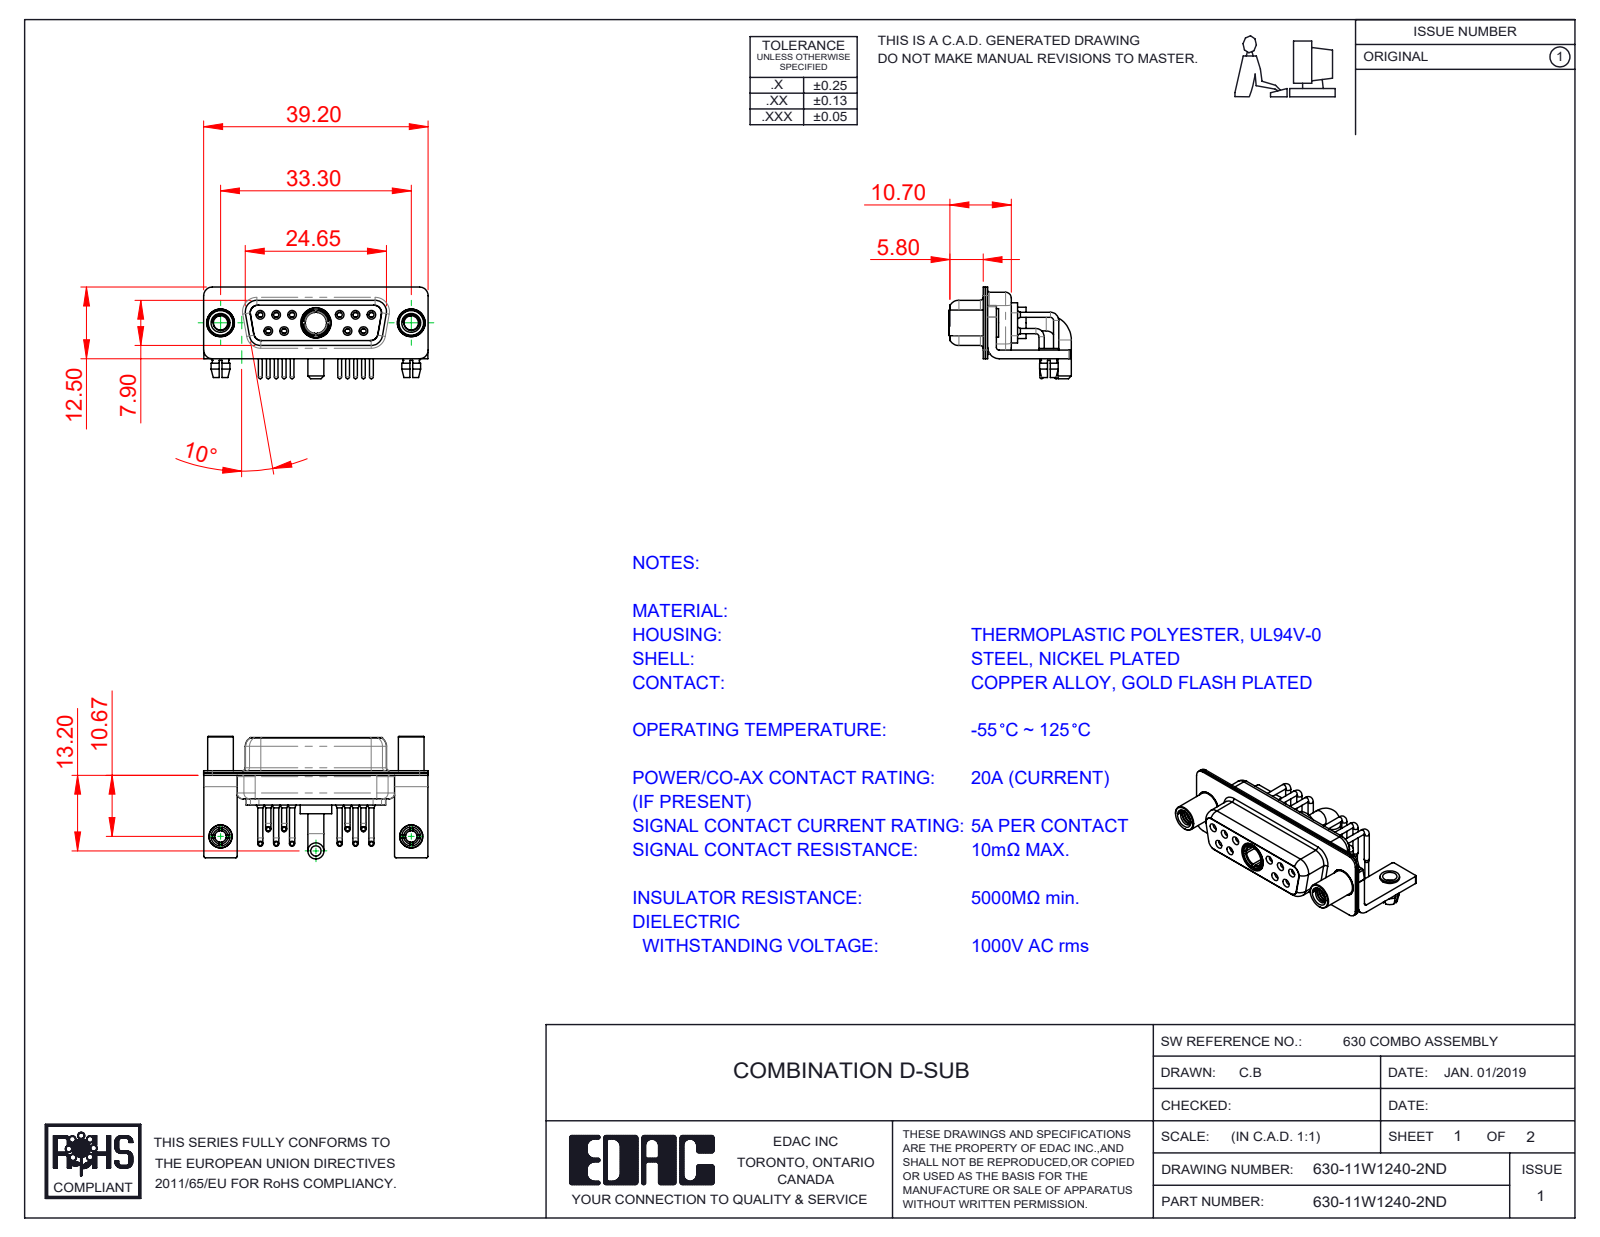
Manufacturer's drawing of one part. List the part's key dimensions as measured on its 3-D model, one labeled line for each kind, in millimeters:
Part name (STEP PRODUCT): 630Combo Threaded Standoff_D; 630Combo Contact Row 1; 630Combo Contact Row 2; Power Socket_20A RA (+6 more)
STEP written by: SolidWorks 2020 (CONFIG_CONTROL_DESIGN)
Units: millimetres
Bodies: 21 solids, 1077 faces (316 planar, 496 cylindrical, 265 other)
Overall size (bounding box): 39.2 × 21.4 × 16
Volume: 3 066 mm³ · Surface area: 7 407 mm²
Round holes (diameter × count): ⌀2 ×12, ⌀0.9 ×10, ⌀1.1 ×10, ⌀1.5 ×10, ⌀1.7 ×6, ⌀1.6 ×4, ⌀2.5 ×4, ⌀4.85 ×3, ⌀3.2 ×2, ⌀4 ×2, ⌀4.05 ×2, ⌀3.7 ×1
Round bosses / shafts (diameter × count): ⌀0.9 ×10, ⌀0.65 ×10, ⌀1.6 ×6, ⌀5 ×2, ⌀4.95 ×2, ⌀4.8 ×2, ⌀4.5 ×2, ⌀4 ×2
Partial cylindrical surfaces — rounded edges, fillets, slot ends (radius × count): R0.25 ×16, R1.5 ×16, R2 ×13, R1.35 ×12, R1.6 ×8, R0.5 ×5, R0.6 ×4, R0.65 ×4
Main face-to-face distances: 0.4, 0.8, 0.45, 1.4, 8.45, 1.5, 1.8, 8.9, 6.2, 2.3
Hole centre spacings: 3.16, 2.77, 13.85, 11.08, 16.62, 5.03, 5.04, 5.54
